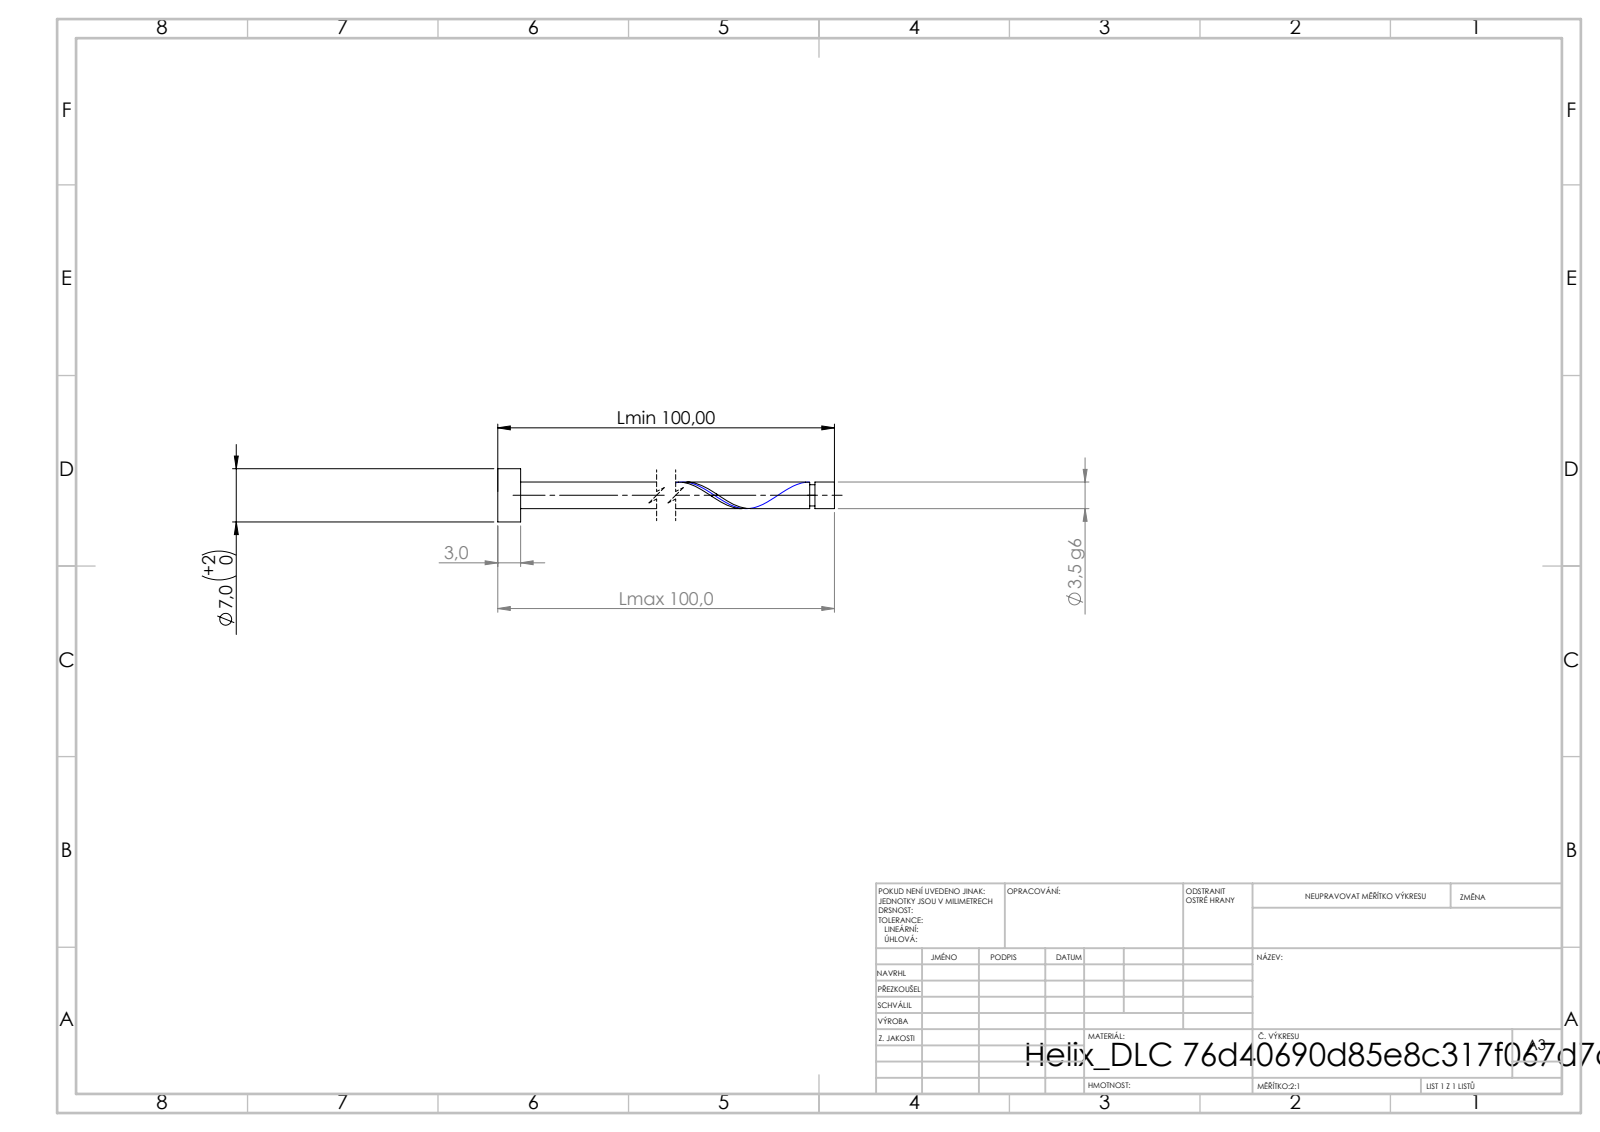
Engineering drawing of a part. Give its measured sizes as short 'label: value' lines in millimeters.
written by: SolidWorks 2019 (CONFIG_CONTROL_DESIGN)
unit: mm
bodies: 1 solid, 21 faces (6 planar, 14 cylindrical, 1 other)
size: 100 × 7 × 7
volume: 1 037 mm³; area: 1 236 mm²
bosses: 1× ⌀7, 1× ⌀3.5, 1× ⌀2.8
face distances: 3, 100, 97, 97.44, 94.44, 2.56, 96.74, 93.74, 0.7, 3.26
